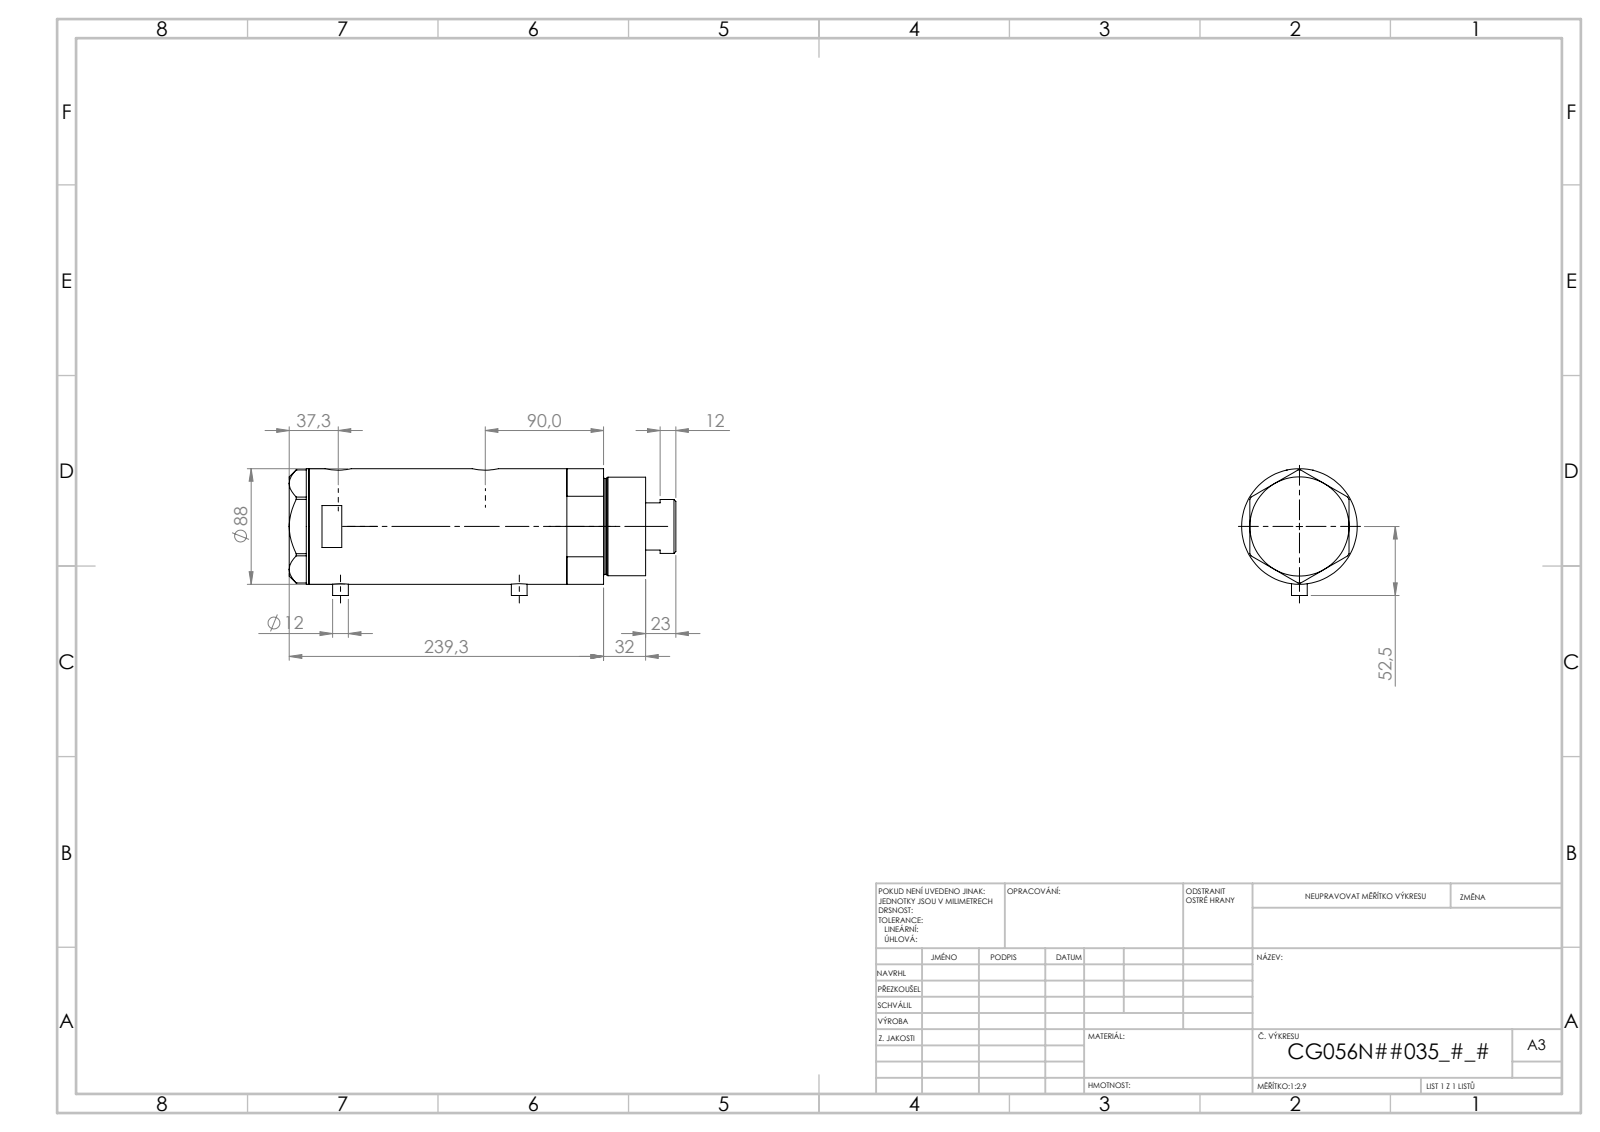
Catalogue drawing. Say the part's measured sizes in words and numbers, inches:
The part is named "V270CG_MIDDLE; V270CG_BACK; V270CG_VC; V270CG_FRONT". Its 3-D file was written by "SolidWorks 2019 (CONFIG_CONTROL_DESIGN)". It is 4 solids with 126 faces: 53 planar, 53 cylindrical and 20 other. Overall it measures 10.215 by 3.508 by 3.465 inches. Its volume is 81.59 cubic inches and its surface area 311.1 square inches. Round holes: 2 of diameter 0.197, 2 of diameter 0.492, 2 of diameter 0.518, 2 of diameter 0.787, 1 of diameter 0.571, 1 of diameter 1.654, 1 of diameter 1.713, 1 of diameter 2.205, 1 of diameter 2.362, 1 of diameter 3.15. Round bosses or shafts: 2 of diameter 0.472, 1 of diameter 3.465, 1 of diameter 2.953, 1 of diameter 2.874, 1 of diameter 1.614. The main face-to-face distances are 4.307, 1.024, 3.283, 0.591, 1.614, 4.898, 8.719, 9.31, 7.696, 4.412. The hole center spacings are 0.067, 1.016, 3.358, 3.425, 4.374, 4.441.
